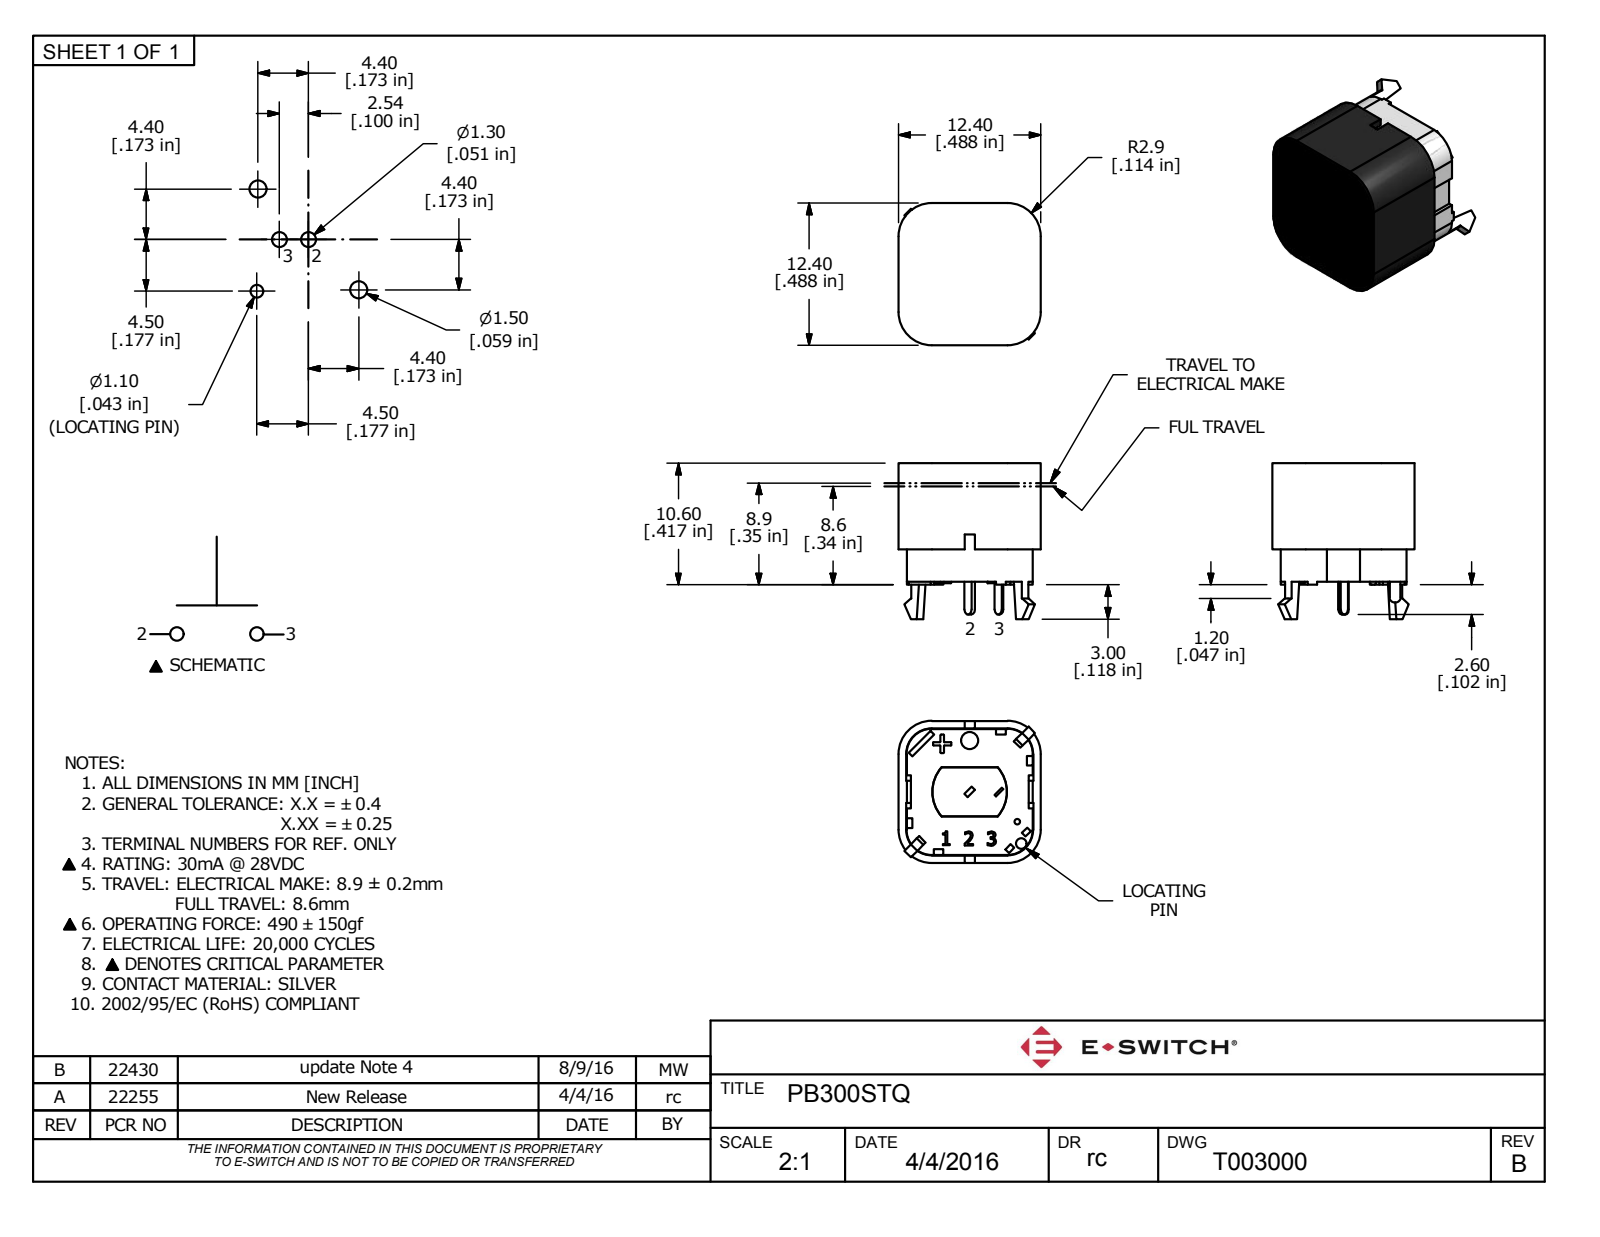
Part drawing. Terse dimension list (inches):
name: P:\\E-Switch Secure\\3D_MODELS_STP_FORMAT\\PB300STQ.stp
written by: ACIS (CONFIG_CONTROL_DESIGN)
unit: in
bodies: 1 solid, 248 faces (160 planar, 44 cylindrical, 44 other)
size: 0.535 × 0.488 × 0.488
volume: 0.071 in³; area: 2.358 in²
holes: 1× ⌀0.059
bosses: 1× ⌀0.037, 1× ⌀0.02
rounds: 4× R0.087, 4× R0.089, 4× R0.114, 2× R0.018, 1× R0.128, 1× R0.128
face distances: 0.028, 0.026, 0.463, 0.461, 0.435, 0.112, 0.295, 0.085, 0.38, 0.407
